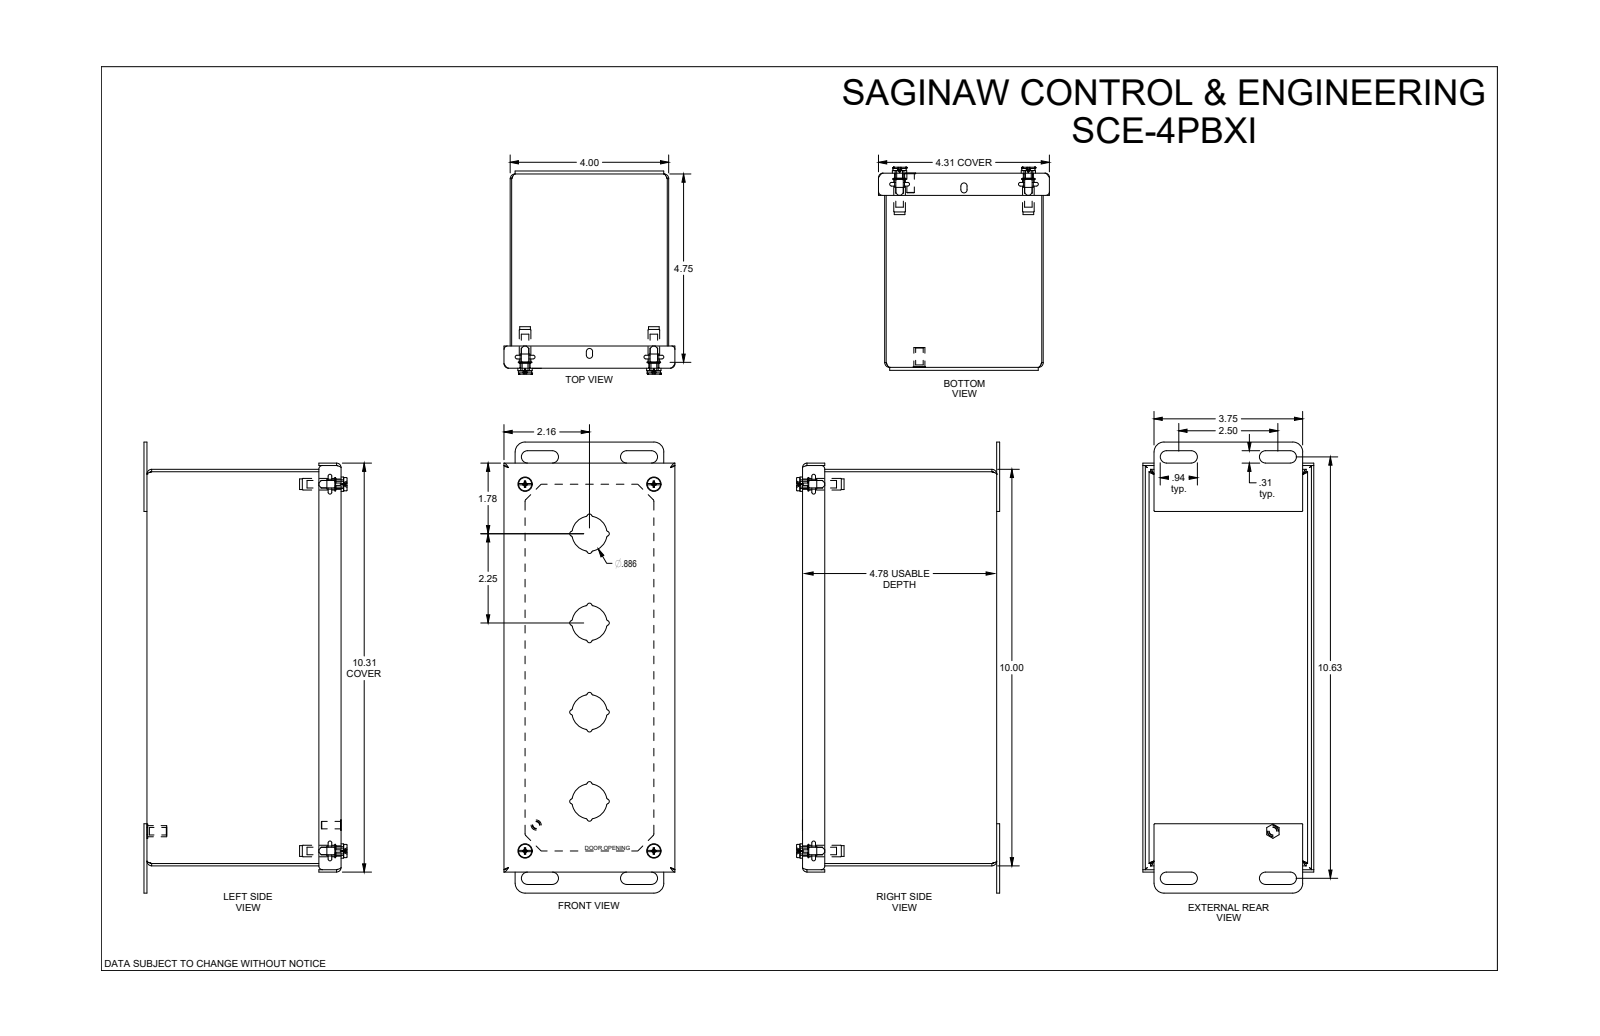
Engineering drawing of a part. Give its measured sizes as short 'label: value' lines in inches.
name: SCE-4PBXI
written by: SolidWorks 2021 (AUTOMOTIVE_DESIGN)
unit: in
bodies: 3 solids, 480 faces (153 planar, 243 cylindrical, 84 other)
size: 11.375 × 5.036 × 4.313
volume: 15.69 in³; area: 506.7 in²
holes: 5× ⌀0.19, 4× ⌀0.22, 4× ⌀0.25, 4× ⌀0.266, 4× ⌀0.317
bosses: 4× ⌀0.362, 4× ⌀0.34, 4× ⌀0.292, 4× ⌀0.27, 4× ⌀0.26, 1× ⌀0.28, 1× ⌀0.256, 1× ⌀0.188
rounds: 32× R0.04, 20× R0.06, 16× R0.062, 8× R0.015, 8× R0.115, 8× R0.156, 8× R0.245, 4× R0.02
face distances: 0.06, 3.94, 4.838, 4, 3.88, 4.778, 9.94, 4.898, 0.156, 4.096
hole spacings: 3.25, 9.25, 9.25, 9.804, 9.804, 3.25, 3.25, 9.172
